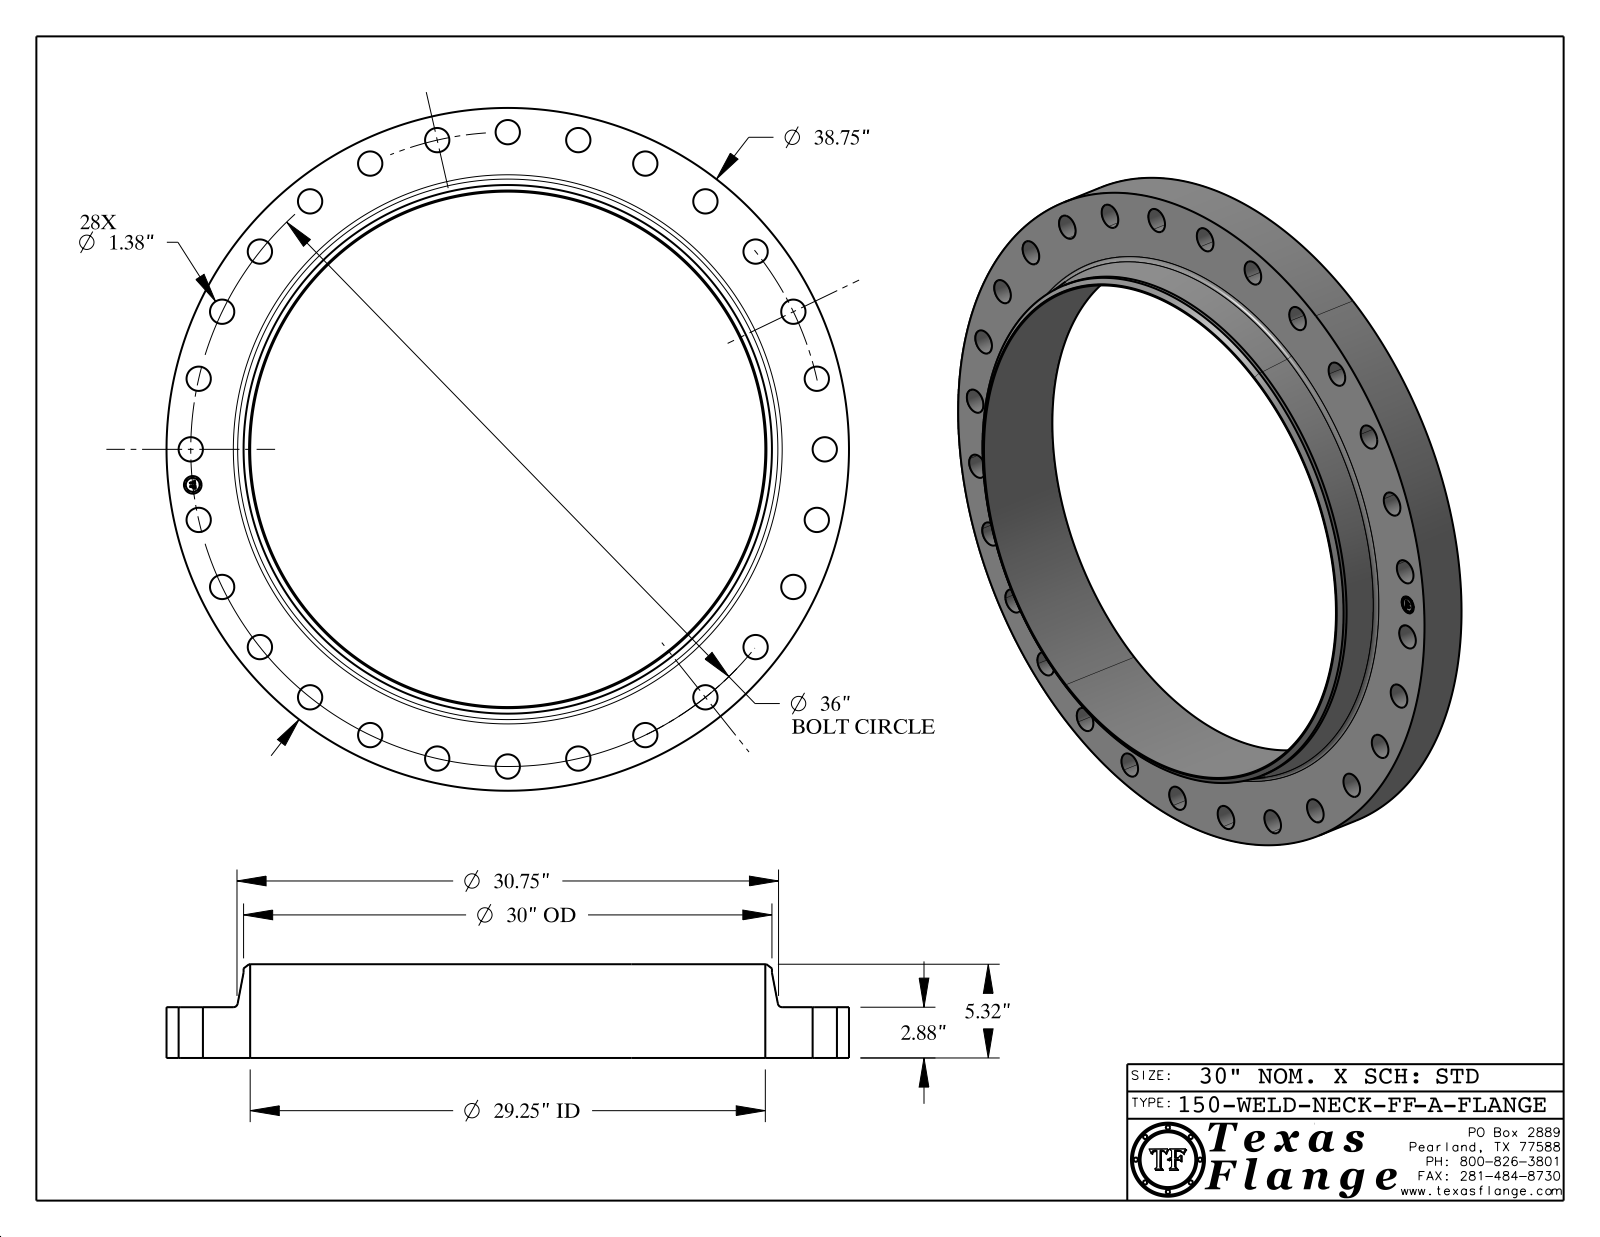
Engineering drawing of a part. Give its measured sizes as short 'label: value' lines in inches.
name: 150-WELD-NECK-FF, Series A
written by: CATIA V5 STEP AP214 (AUTOMOTIVE_DESIGN)
unit: in
bodies: 1 solid, 456 faces (368 planar, 82 cylindrical, 6 other)
size: 38.75 × 38.75 × 5.32
volume: 1 458 in³; area: 2 299 in²
holes: 28× ⌀1.38, 1× ⌀1, 1× ⌀29.25
bosses: 8× ⌀0.061, 1× ⌀38.75, 1× ⌀30, 1× ⌀0.788
face distances: 2.88, 5.32, 2.44, 0.015, 2.865, 2.455, 0.298, 0.293, 0.054, 0.193
hole spacings: 18, 19.153, 4.031, 8.011, 11.89, 15.62, 22.446, 25.456
